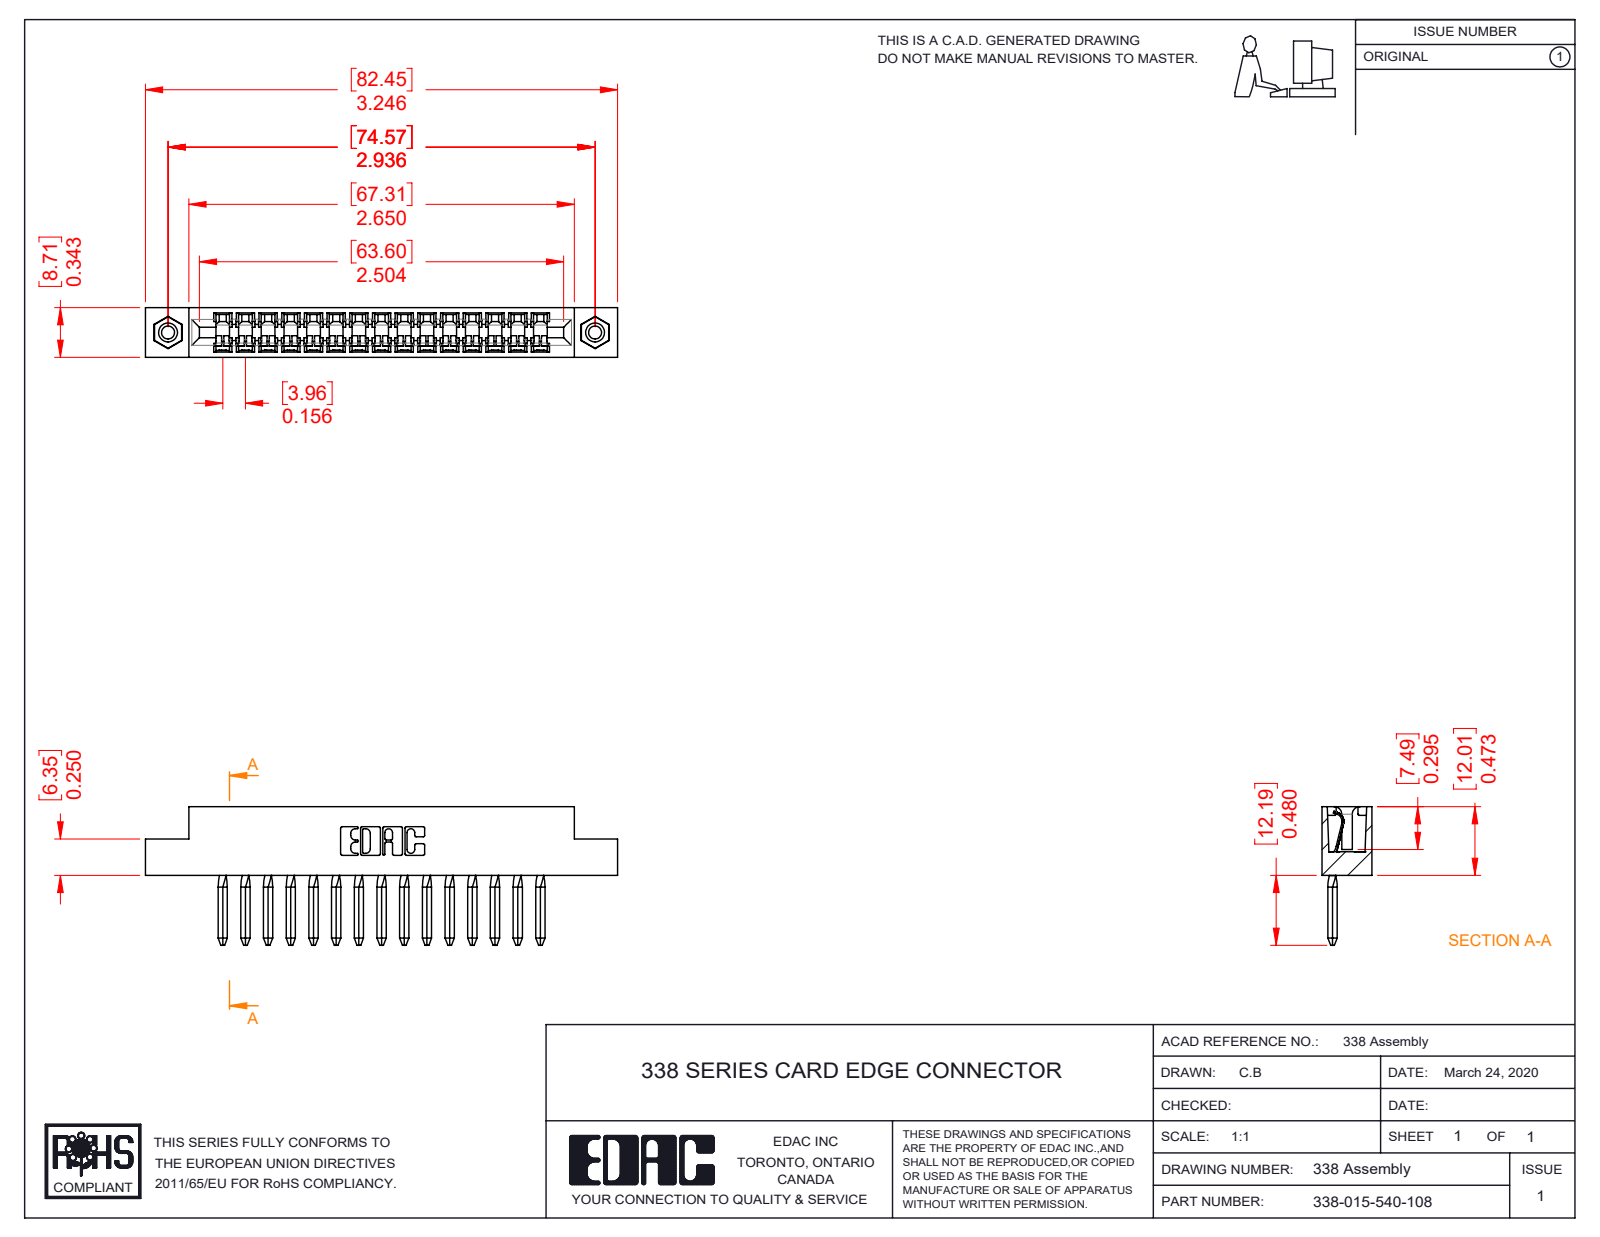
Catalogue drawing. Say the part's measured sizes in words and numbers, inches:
The part is named "338-290-001_540; 338-210-001_338-210-015-004; 338-015-540-108; 345-250-001_345-250-003-102". Its 3-D file was written by "SolidWorks 2016 (CONFIG_CONTROL_DESIGN)". It is 18 solids with 1549 faces: 1057 planar, 416 cylindrical and 76 other. Overall it measures 3.246 by 0.953 by 0.343 inches. Its volume is 0.342 cubic inches and its surface area 13.21 square inches. Round holes: 2 of diameter 0.089, 2 of diameter 0.125, 2 of diameter 0.156. Round bosses or shafts: 2 of diameter 0.155. Partial cylindrical surfaces (rounded edges, fillets, slot ends): 62 of radius 0.025, 22 of radius 0.01, 15 of radius 0.008, 12 of radius 0.055, 12 of radius 0.067, 12 of radius 0.1, 6 of radius 0.007, 6 of radius 0.031. The main face-to-face distances are 0.343, 0.156, 0.624, 0.468, 0.78, 0.207, 0.135, 0.312, 0.11, 0.312. The hole center spacings are 2.936.
